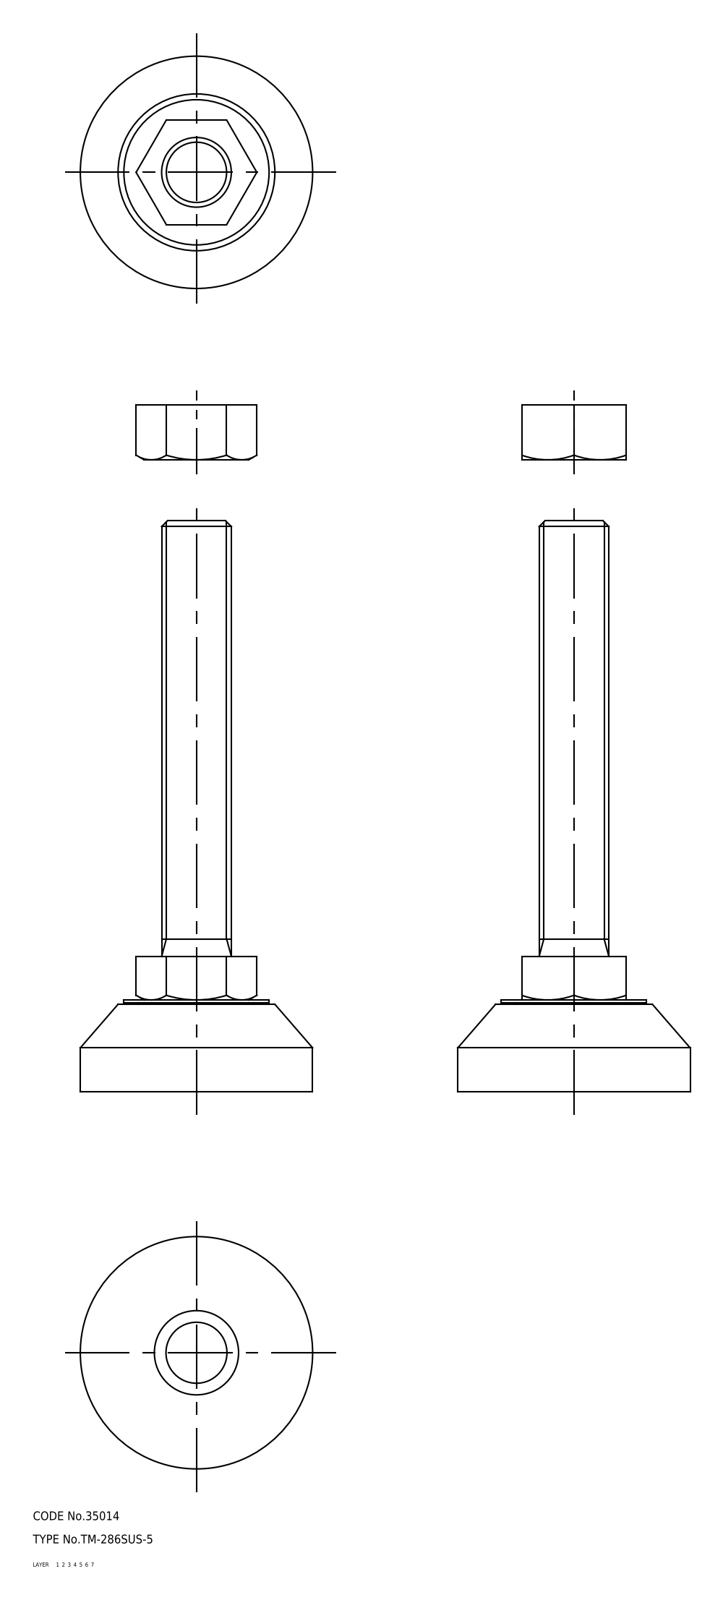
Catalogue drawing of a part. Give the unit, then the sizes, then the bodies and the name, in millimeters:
Units: millimetres
Overall size (bounding box): 196.5 × 80 × 80
Volume: 225 821 mm³ · Surface area: 36 163 mm²
Bodies: 2 solids, 52 faces (0 planar, 0 cylindrical, 52 other)
Part name (STEP PRODUCT): 67111650; 67111663
STEP written by: CADfix (AUTOMOTIVE_DESIGN)
